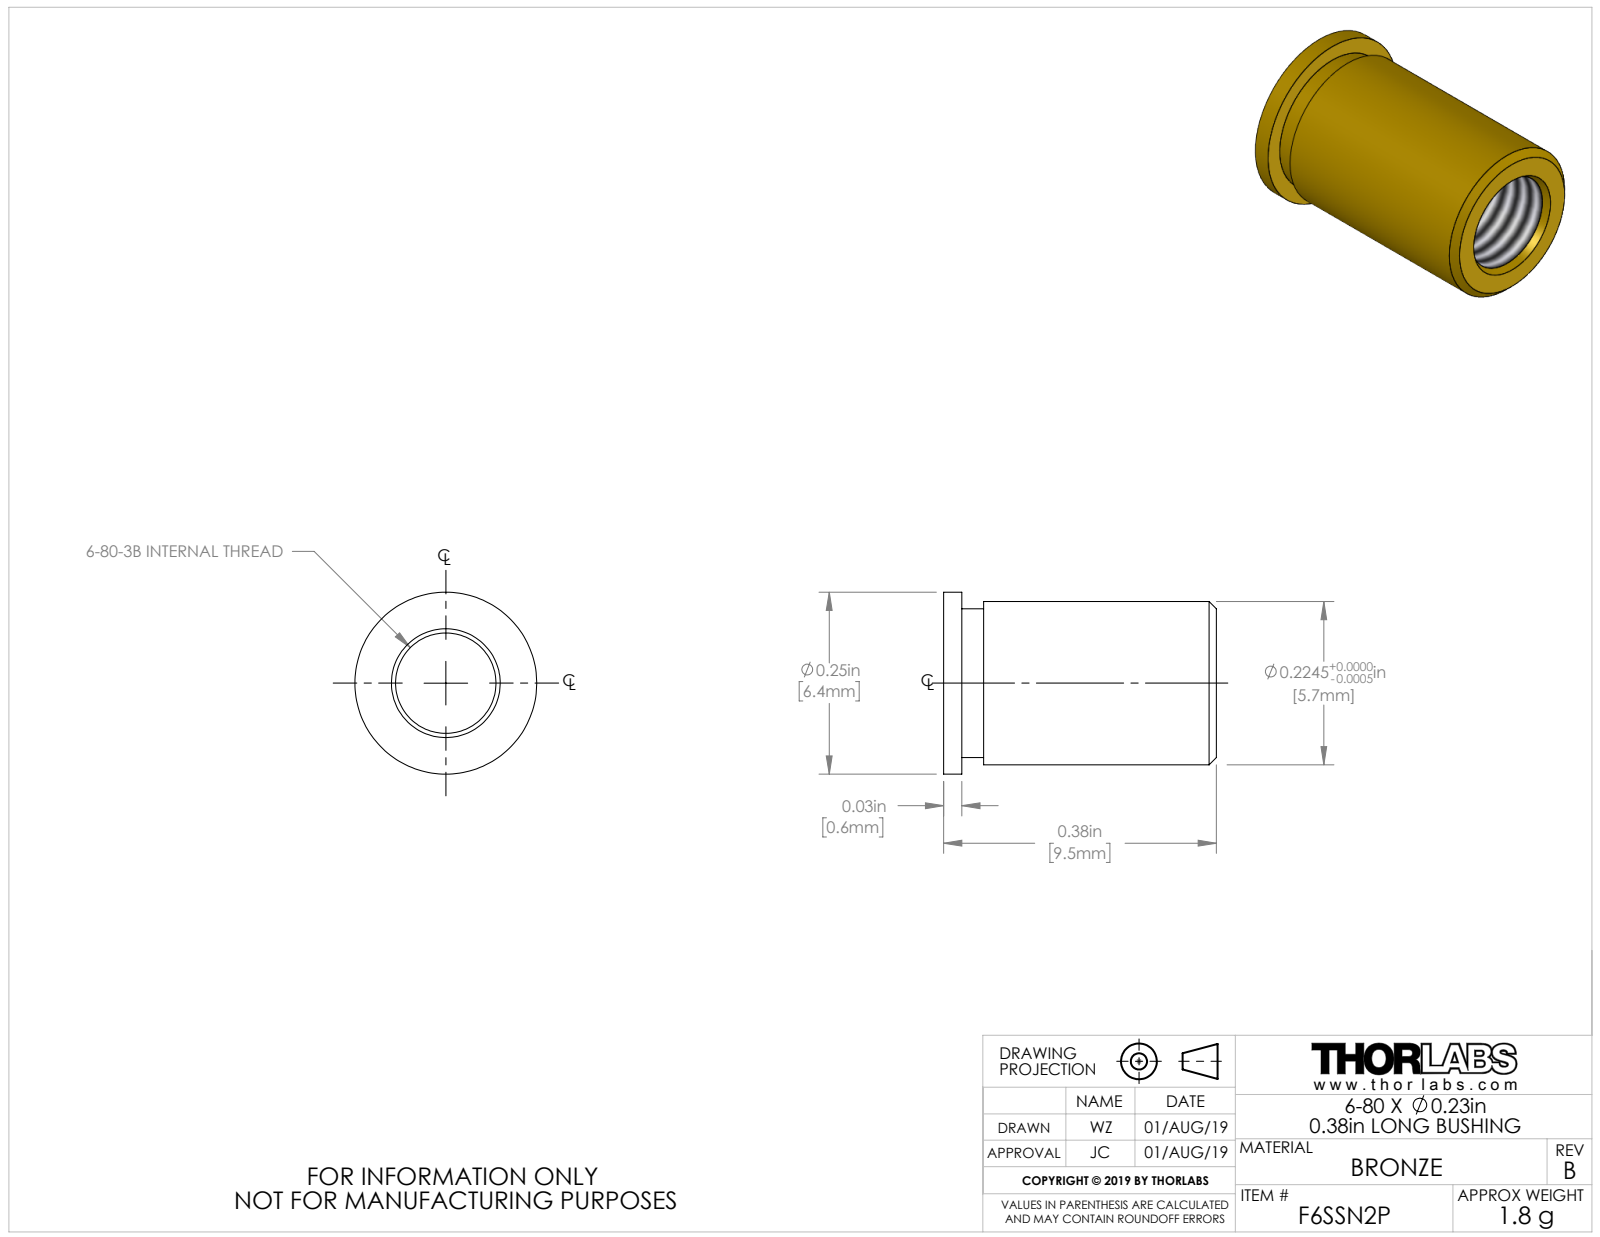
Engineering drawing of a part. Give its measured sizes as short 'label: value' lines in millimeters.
name: 18999-E0W
written by: SolidWorks 2007 (AUTOMOTIVE_DESIGN)
unit: mm
bodies: 1 solid, 18 faces (4 planar, 8 cylindrical, 6 other)
size: 9.53 × 6.35 × 6.35
volume: 151 mm³; area: 323 mm²
holes: 1× ⌀3.51
bosses: 1× ⌀6.35, 1× ⌀5.7, 1× ⌀5.19
face distances: 0.63, 9.52, 8.89, 1.39, 0.76, 8.13
